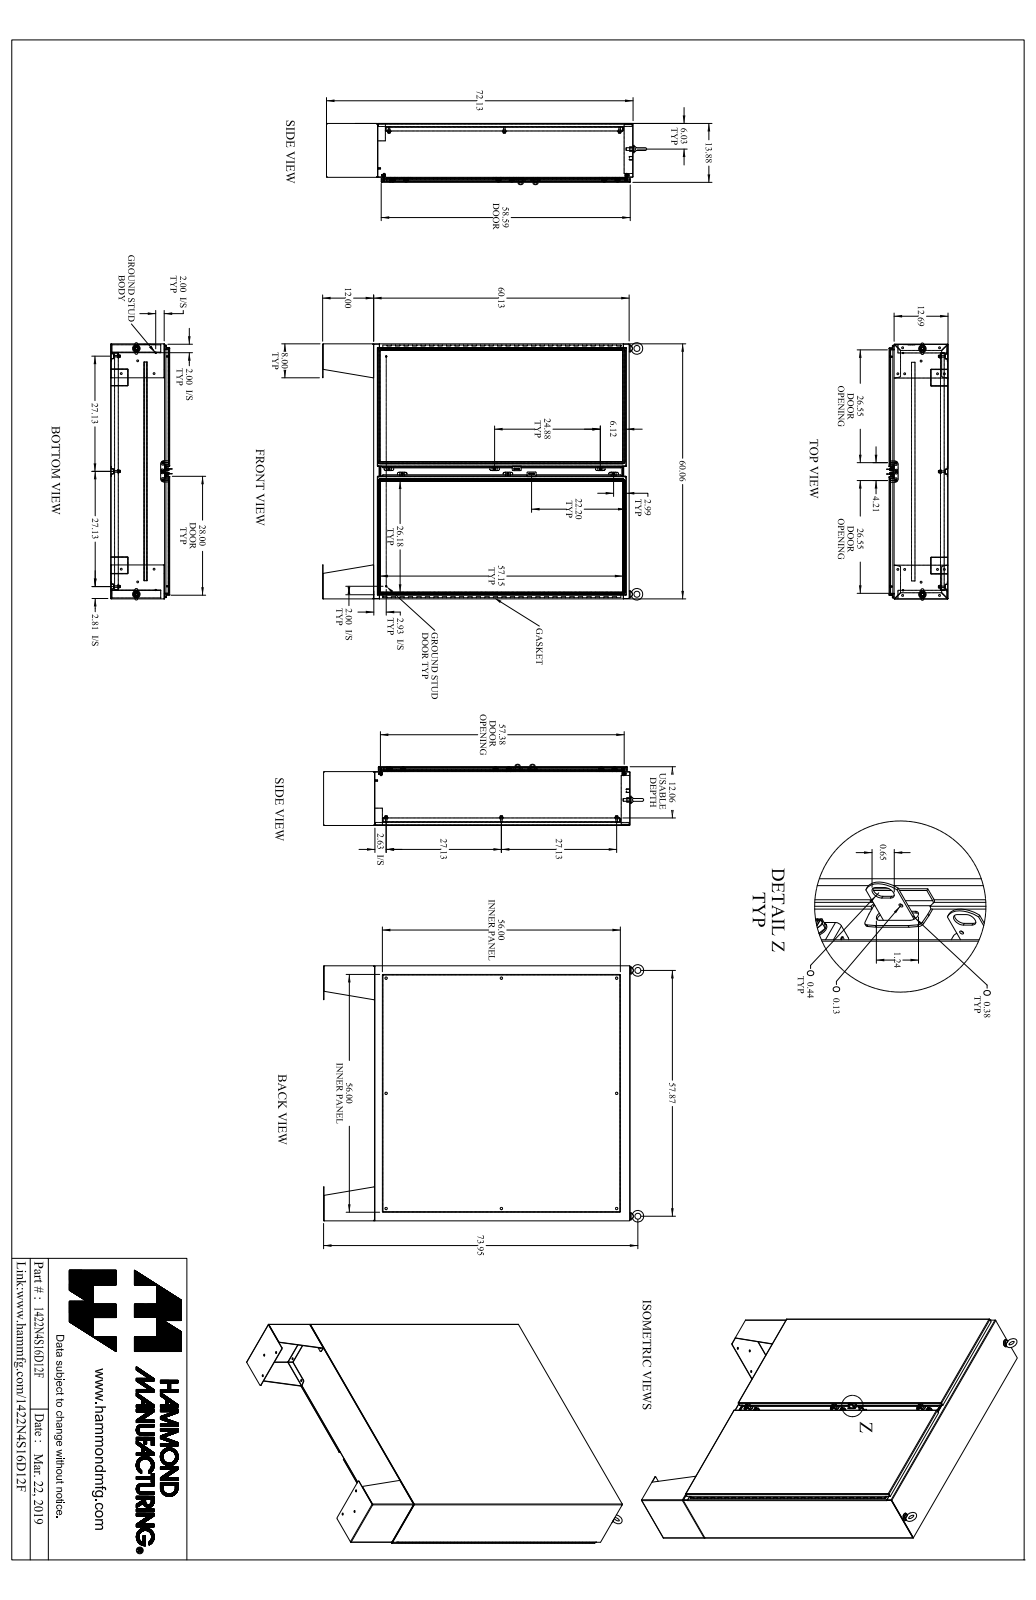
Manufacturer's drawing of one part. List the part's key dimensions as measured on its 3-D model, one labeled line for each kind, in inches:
Part name (STEP PRODUCT): 1422N4S16D12F_Default
STEP written by: SolidWorks 2019 (CONFIG_CONTROL_DESIGN)
Units: inches
Bodies: 107 solids, 3246 faces (1582 planar, 1444 cylindrical, 220 other)
Overall size (bounding box): 75.784 × 61.121 × 14.438
Volume: 1 680 in³ · Surface area: 34 076 in²
Round holes (diameter × count): ⌀0.304 ×20, ⌀0.437 ×14, ⌀0.307 ×8, ⌀0.563 ×8, ⌀0.213 ×6, ⌀0.265 ×6, ⌀0.375 ×6, ⌀0.445 ×6, ⌀0.201 ×3, ⌀0.25 ×3, ⌀0.313 ×3, ⌀0.11 ×2
Round bosses / shafts (diameter × count): ⌀1 ×8, ⌀0.65 ×8, ⌀0.375 ×8, ⌀0.332 ×8, ⌀0.5 ×6, ⌀0.39 ×6, ⌀0.244 ×6, ⌀0.313 ×4
Partial cylindrical surfaces — rounded edges, fillets, slot ends (radius × count): R0.048 ×67, R0.143 ×67, R0.25 ×34, R0.06 ×18, R0.116 ×12, R0.141 ×12, R0.125 ×10, R0.05 ×8
Main face-to-face distances: 0.095, 13.78, 13.685, 13.875, 0.125, 11.998, 12.093, 1.687, 1.782, 12.218
Hole centre spacings: 6, 58.491, 12, 18, 24, 30, 58.183, 36
